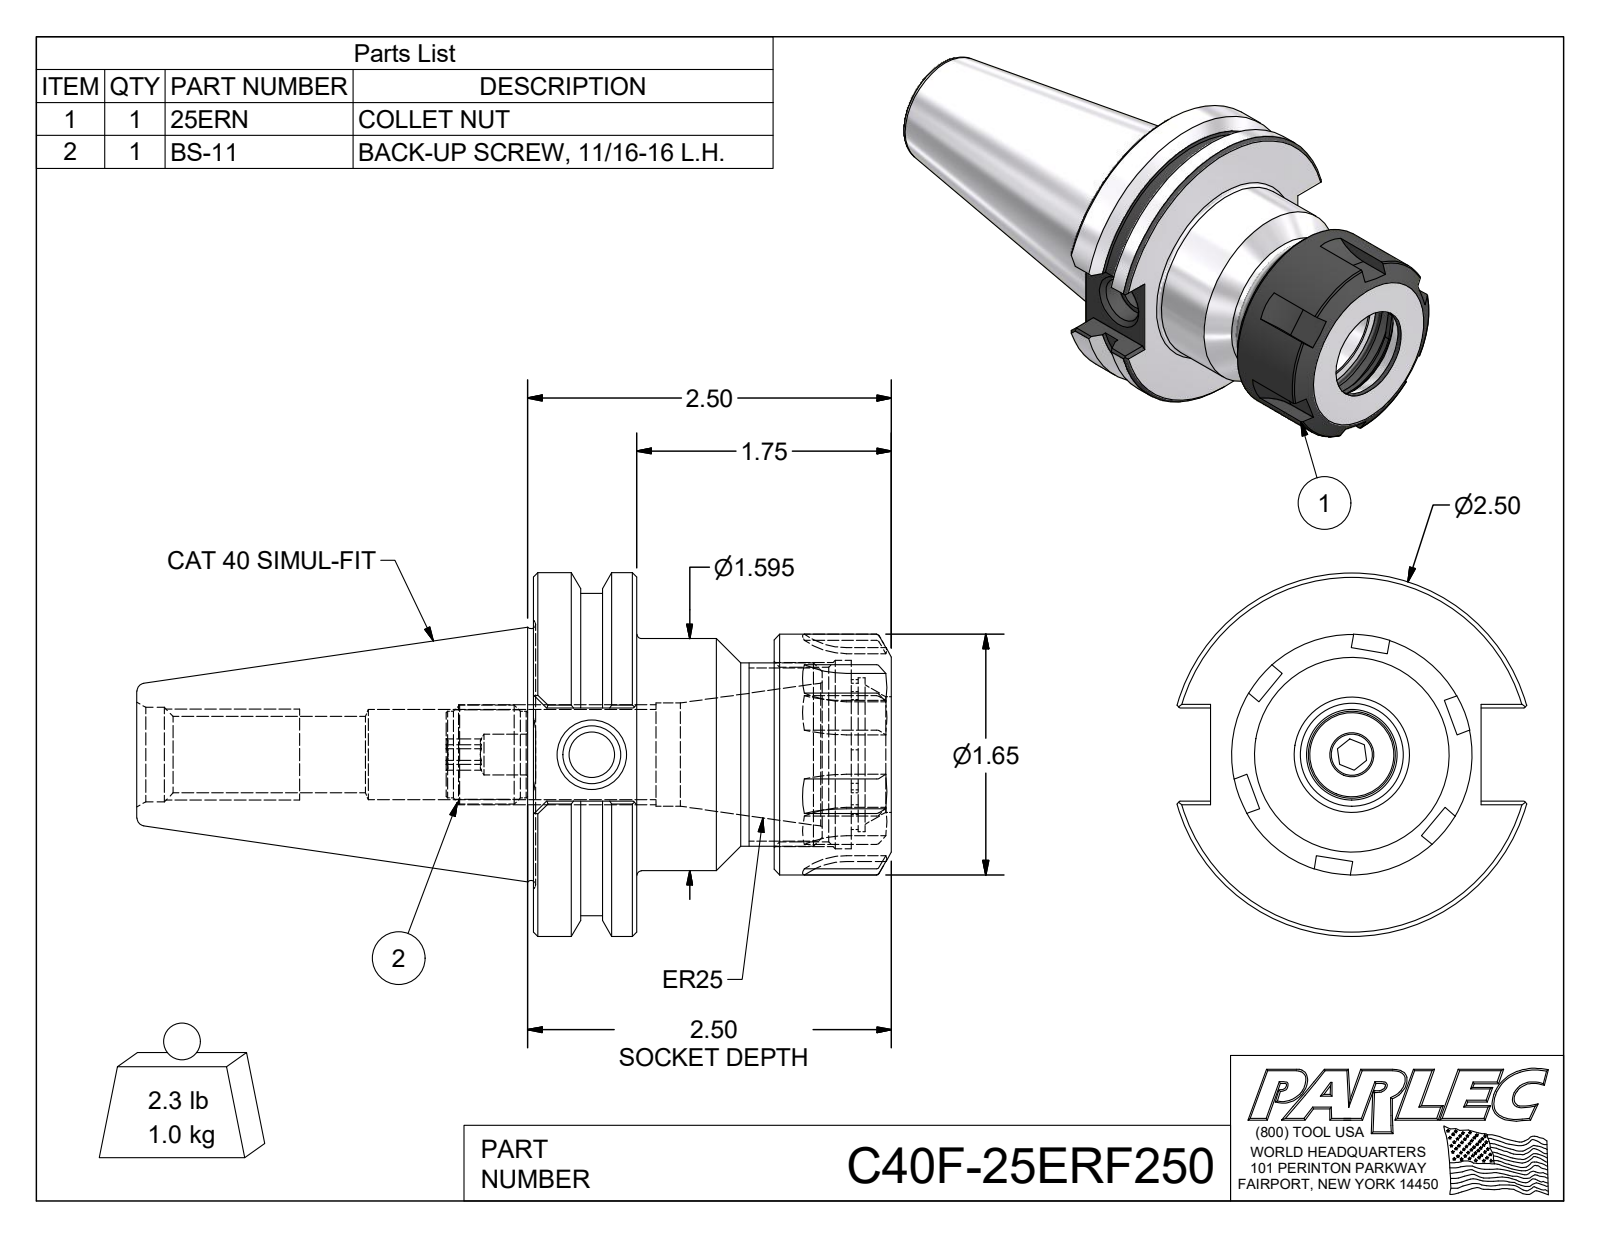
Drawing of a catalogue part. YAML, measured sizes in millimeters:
part_name: "C40F-25ER2-1; 25ERN; BS-11; C40F-25ERF250"
step_written_by: "Autodesk Inventor 2016 (AUTOMOTIVE_DESIGN)"
units: millimeters
bodies: {solids: 3, faces: 175, planar: 75, cylindrical: 37, other: 63}
overall_size: [131.76, 63.5, 61.11]
volume: 139561
surface_area: 33949
round_holes:
  - {diameter: 7.11, count: 1}
  - {diameter: 8, count: 1}
  - {diameter: 10.13, count: 1}
  - {diameter: 13.39, count: 1}
  - {diameter: 15.75, count: 1}
  - {diameter: 16.46, count: 1}
  - {diameter: 18.03, count: 1}
  - {diameter: 20.32, count: 1}
  - {diameter: 30.5, count: 1}
  - {diameter: 32.88, count: 1}
round_bosses_or_shafts:
  - {diameter: 63.5, count: 1}
  - {diameter: 56.26, count: 1}
  - {diameter: 42, count: 1}
  - {diameter: 40.51, count: 1}
  - {diameter: 32, count: 1}
  - {diameter: 17.3, count: 1}
  - {diameter: 15.11, count: 1}
partial_cylinders:
  - {radius: 0.51, count: 12}
  - {radius: 12, count: 1}
  - {radius: 13.06, count: 1}
  - {radius: 13.43, count: 1}
face_to_face_distances: [18.04, 62.49, 44.45, 41.92, 23.88, 20.57, 55.39, 37.35, 13.47, 7.1]
